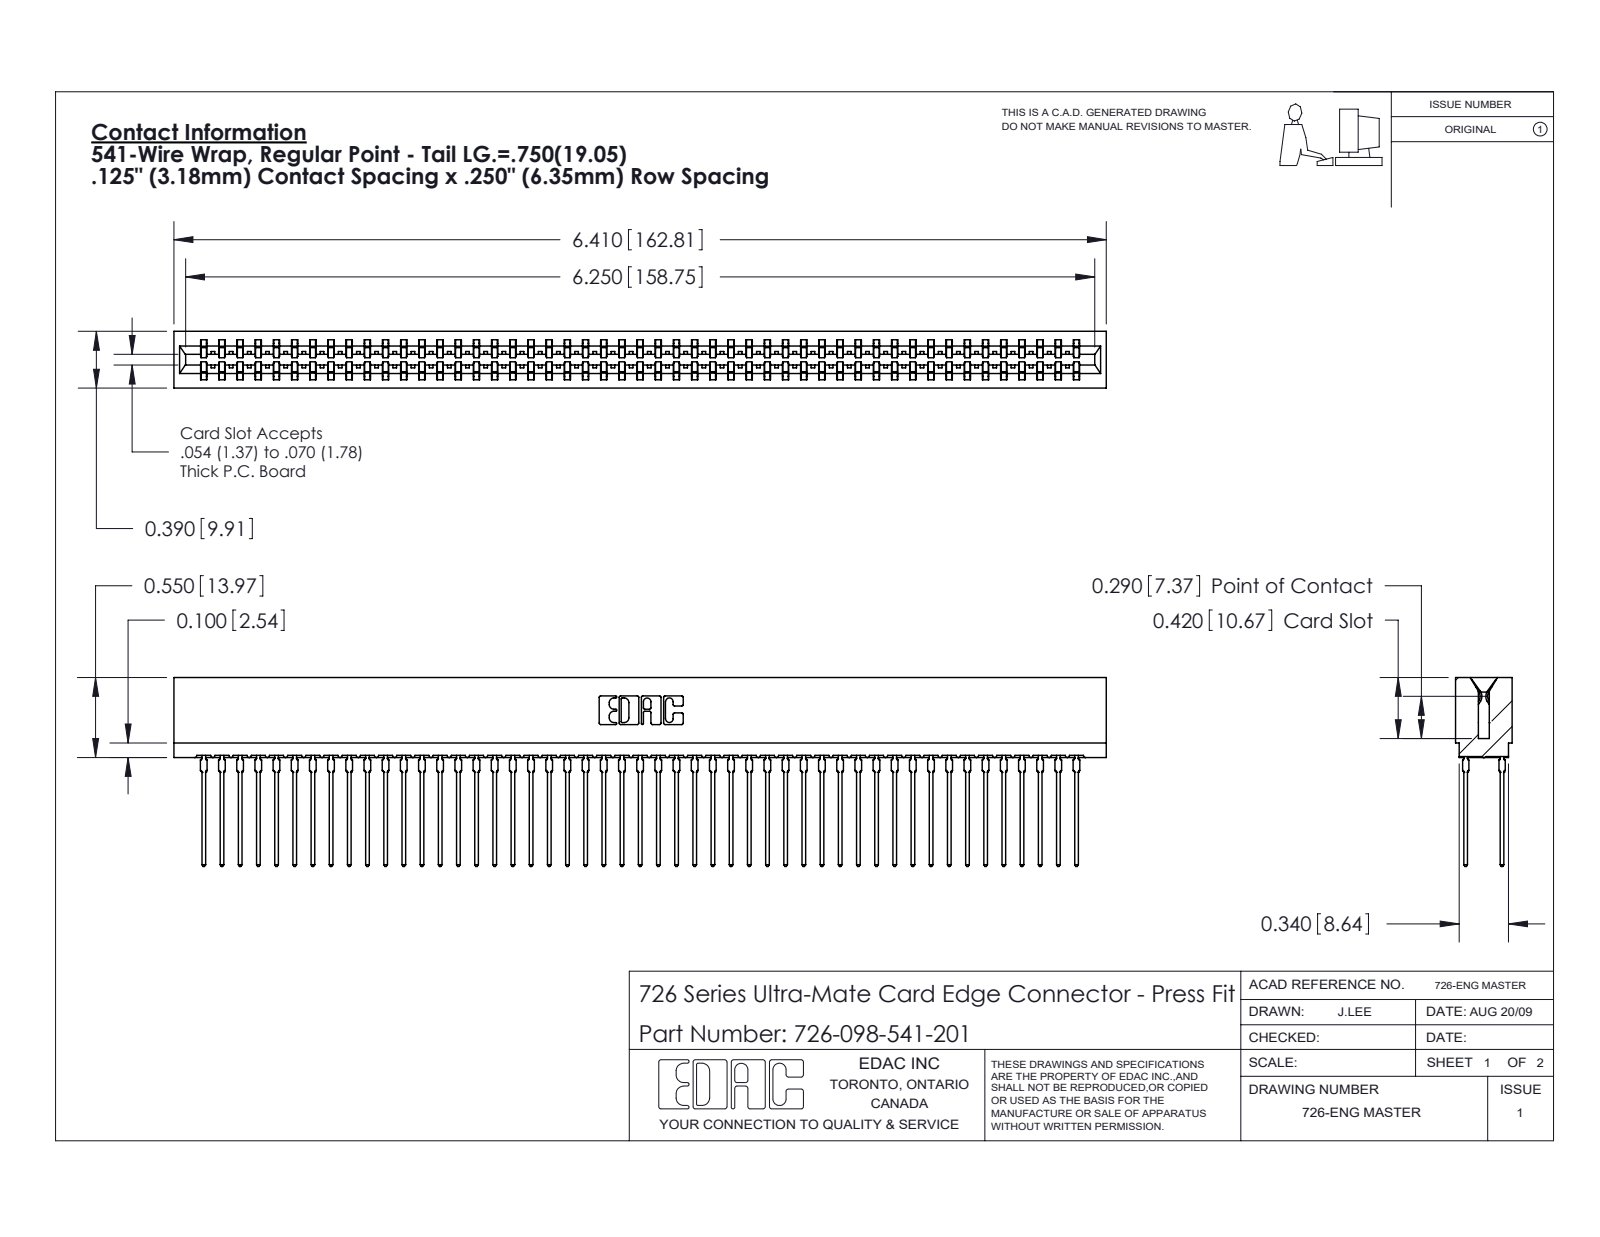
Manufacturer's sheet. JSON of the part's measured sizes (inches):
{"part_name": "726 Part_.515 Slot Depth - 01; 746-292-001_541; 726-098-541-201", "step_written_by": "SolidWorks 2020 (CONFIG_CONTROL_DESIGN)", "units": "inches", "bodies": {"solids": 99, "faces": 8868, "planar": 4563, "cylindrical": 1757, "other": 2548}, "overall_size": [6.41, 1.299, 0.39], "volume_in3": 0.945, "surface_area_in2": 44.07, "partial_cylinders_radius": [[0.021, 196], [0.015, 50], [0.01, 22], [0.005, 8], [0.011, 8], [0.007, 6], [0.031, 6], [0.026, 3]], "face_to_face_distances": [0.057, 0.333, 0.025, 0.307, 0.25, 0.39, 0.083, 0.275, 0.225, 0.365]}
